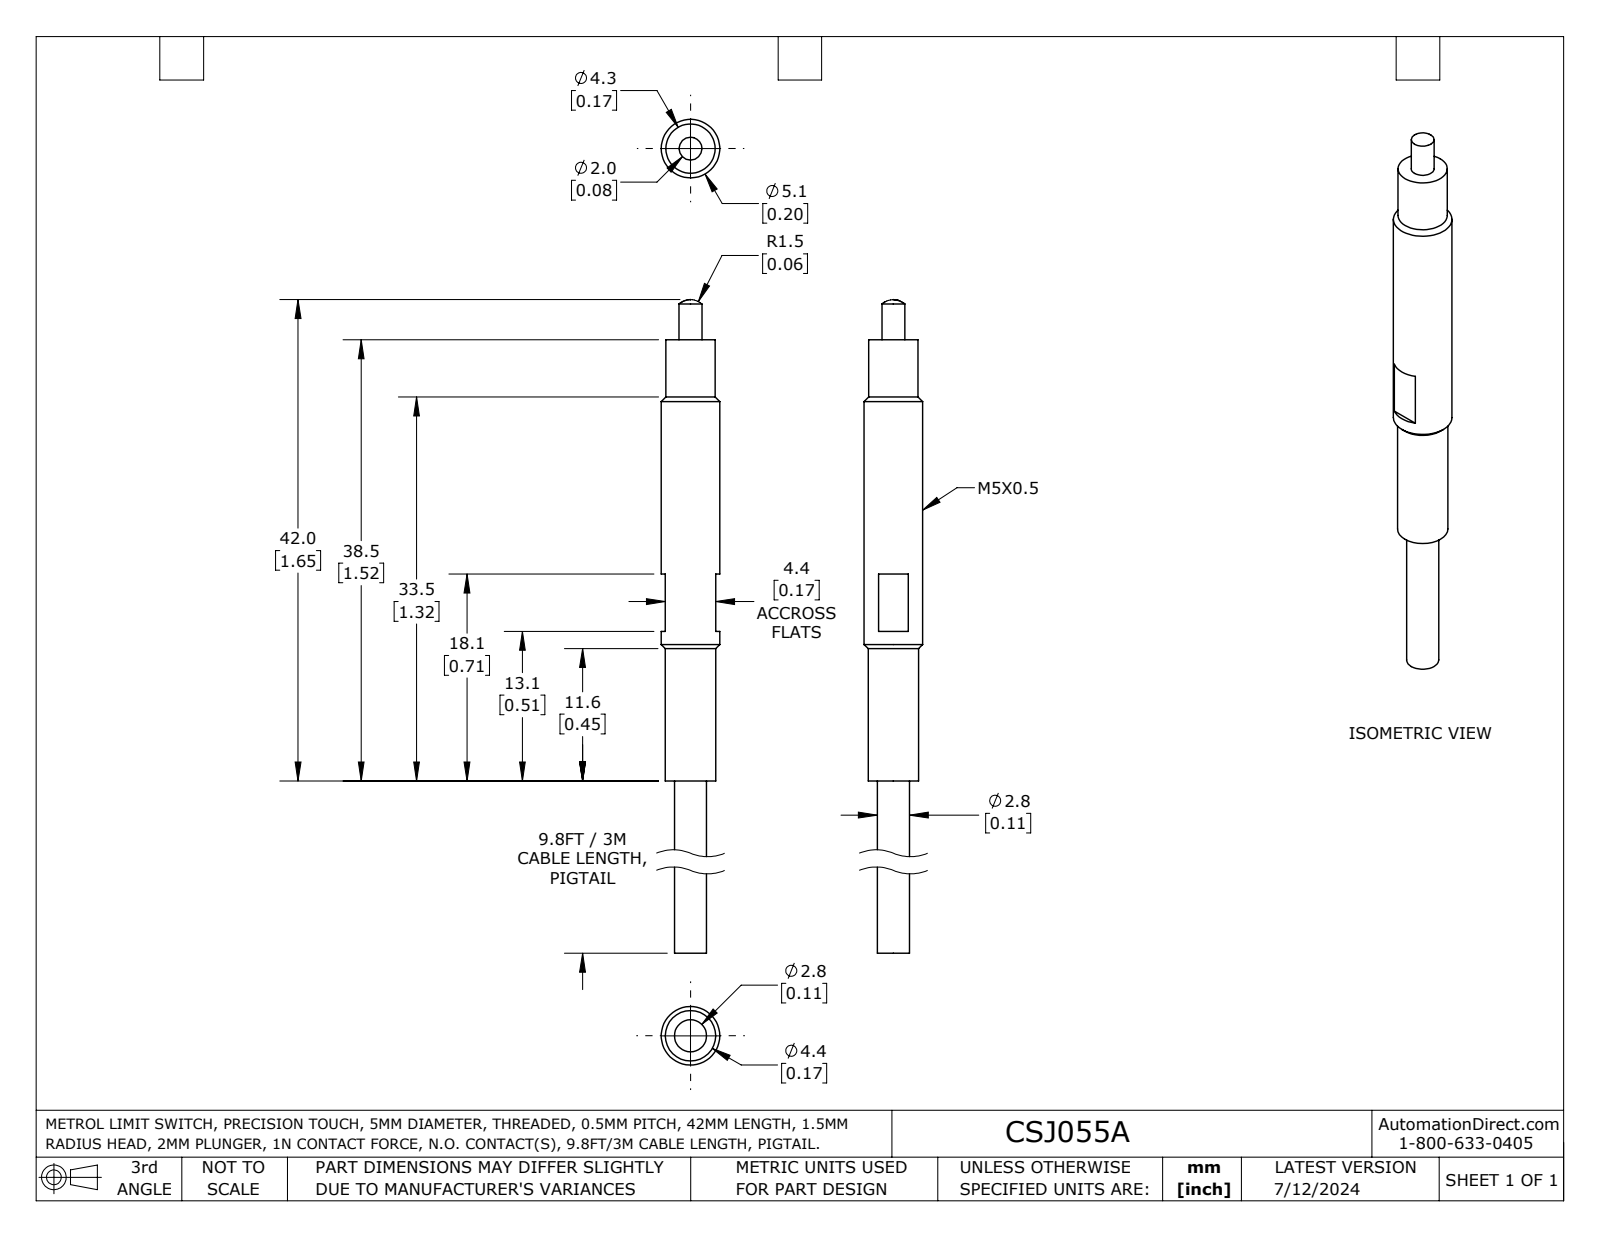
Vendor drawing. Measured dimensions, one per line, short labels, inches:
name: CSJ055A
written by: SolidWorks 2023 (AUTOMOTIVE_DESIGN)
unit: in
bodies: 1 solid, 20 faces (9 planar, 7 cylindrical, 4 other)
size: 2.205 × 0.201 × 0.201
volume: 0.048 in³; area: 1.174 in²
bosses: 1× ⌀0.201, 1× ⌀0.173, 1× ⌀0.169, 1× ⌀0.11, 1× ⌀0.079
face distances: 0.173, 1.516, 0.551, 2.067, 1.262, 0.711, 0.805, 1.065, 0.514, 0.197
